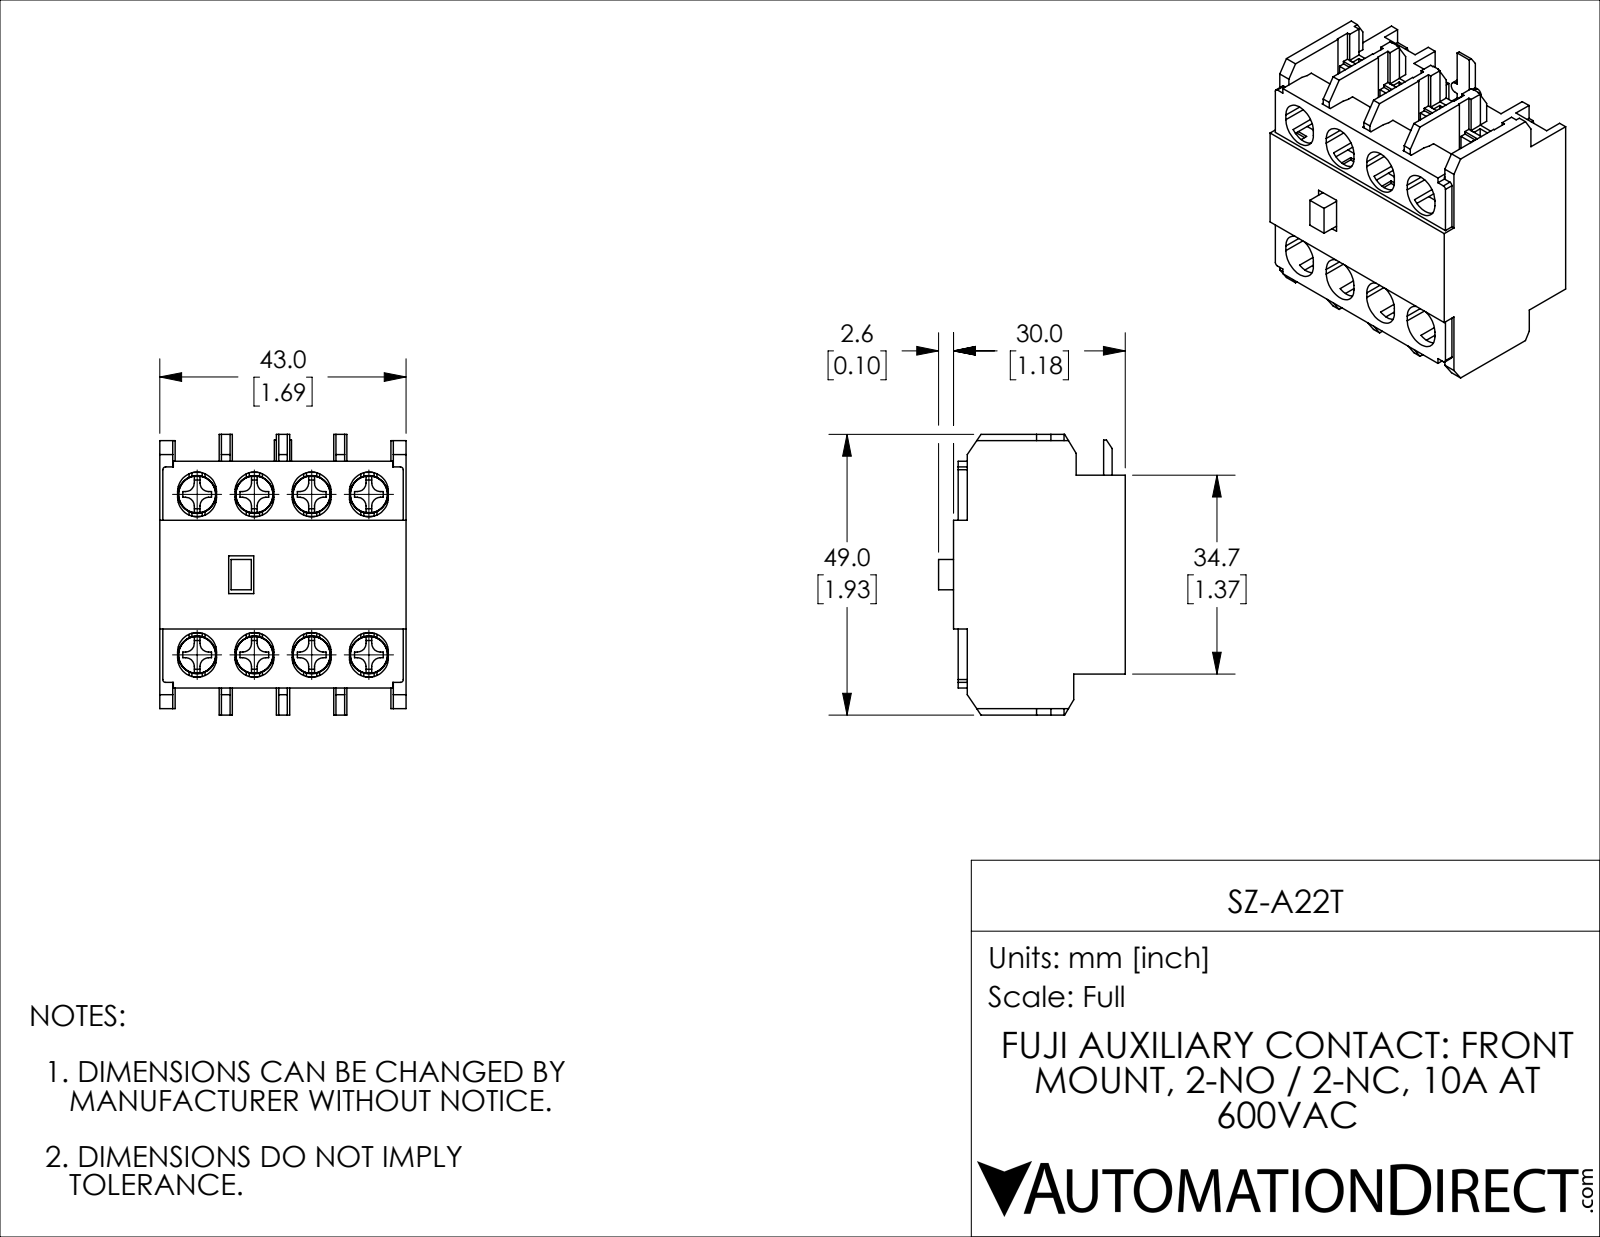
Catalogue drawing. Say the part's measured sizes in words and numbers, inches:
The part is named "SZ-A22T". Its 3-D file was written by "SolidWorks 2019 (CONFIG_CONTROL_DESIGN)". It is 31 solids with 1480 faces: 1266 planar, 166 cylindrical and 48 other. Overall it measures 1.929 by 1.693 by 1.283 inches. Its volume is 1.763 cubic inches and its surface area 39.7 square inches. Round holes: 8 of diameter 0.138, 8 of diameter 0.142. Round bosses or shafts: 8 of diameter 0.26. Partial cylindrical surfaces (rounded edges, fillets, slot ends): 32 of radius 0.059, 16 of radius 0.134, 16 of radius 0.165, 4 of radius 0.02, 2 of radius 0.039. The main face-to-face distances are 0.059, 0.394, 0.423, 0.787, 0.335, 0.039, 0.02, 0.728, 1.27, 0.817. The hole center spacings are 0.394, 1.17, 0.787, 1.102, 1.355, 1.181, 1.616.
